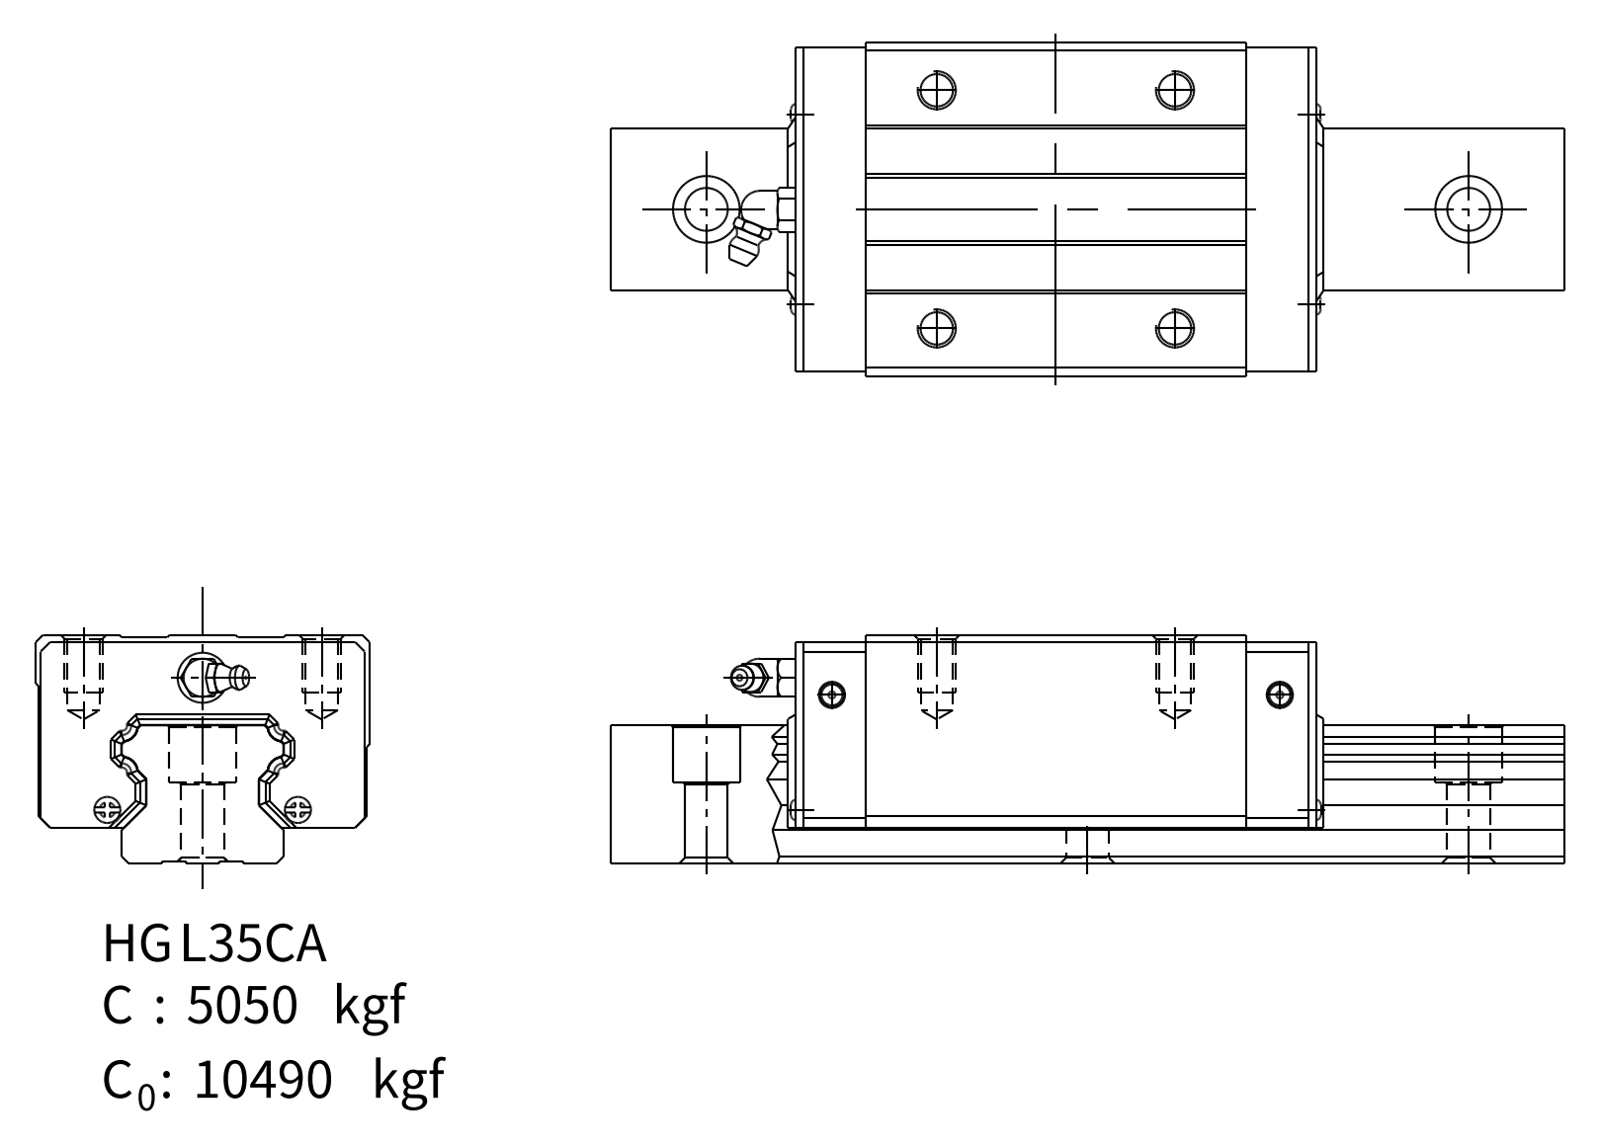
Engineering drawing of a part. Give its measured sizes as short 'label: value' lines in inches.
name: HGH35C_ASM_ASM_Standard; HGH35_ASM_2_ASM_ASM_Standard; HGL35C; HGH35_1_Standard
written by: SolidWorks 2006104 (CONFIG_CONTROL_DESIGN)
unit: in
bodies: 1 solid, 373 faces (297 planar, 16 cylindrical, 60 other)
size: 4.437 × 2.756 × 1.594
volume: 14.63 in³; area: 54.68 in²
holes: 4× ⌀0.315
rounds: 4× R0.047, 4× R0.128
face distances: 1.594, 0.02, 0.846, 0.748, 0.037, 2.736, 4.425, 0.057, 1.537, 0.691
hole spacings: 1.969, 2.784
